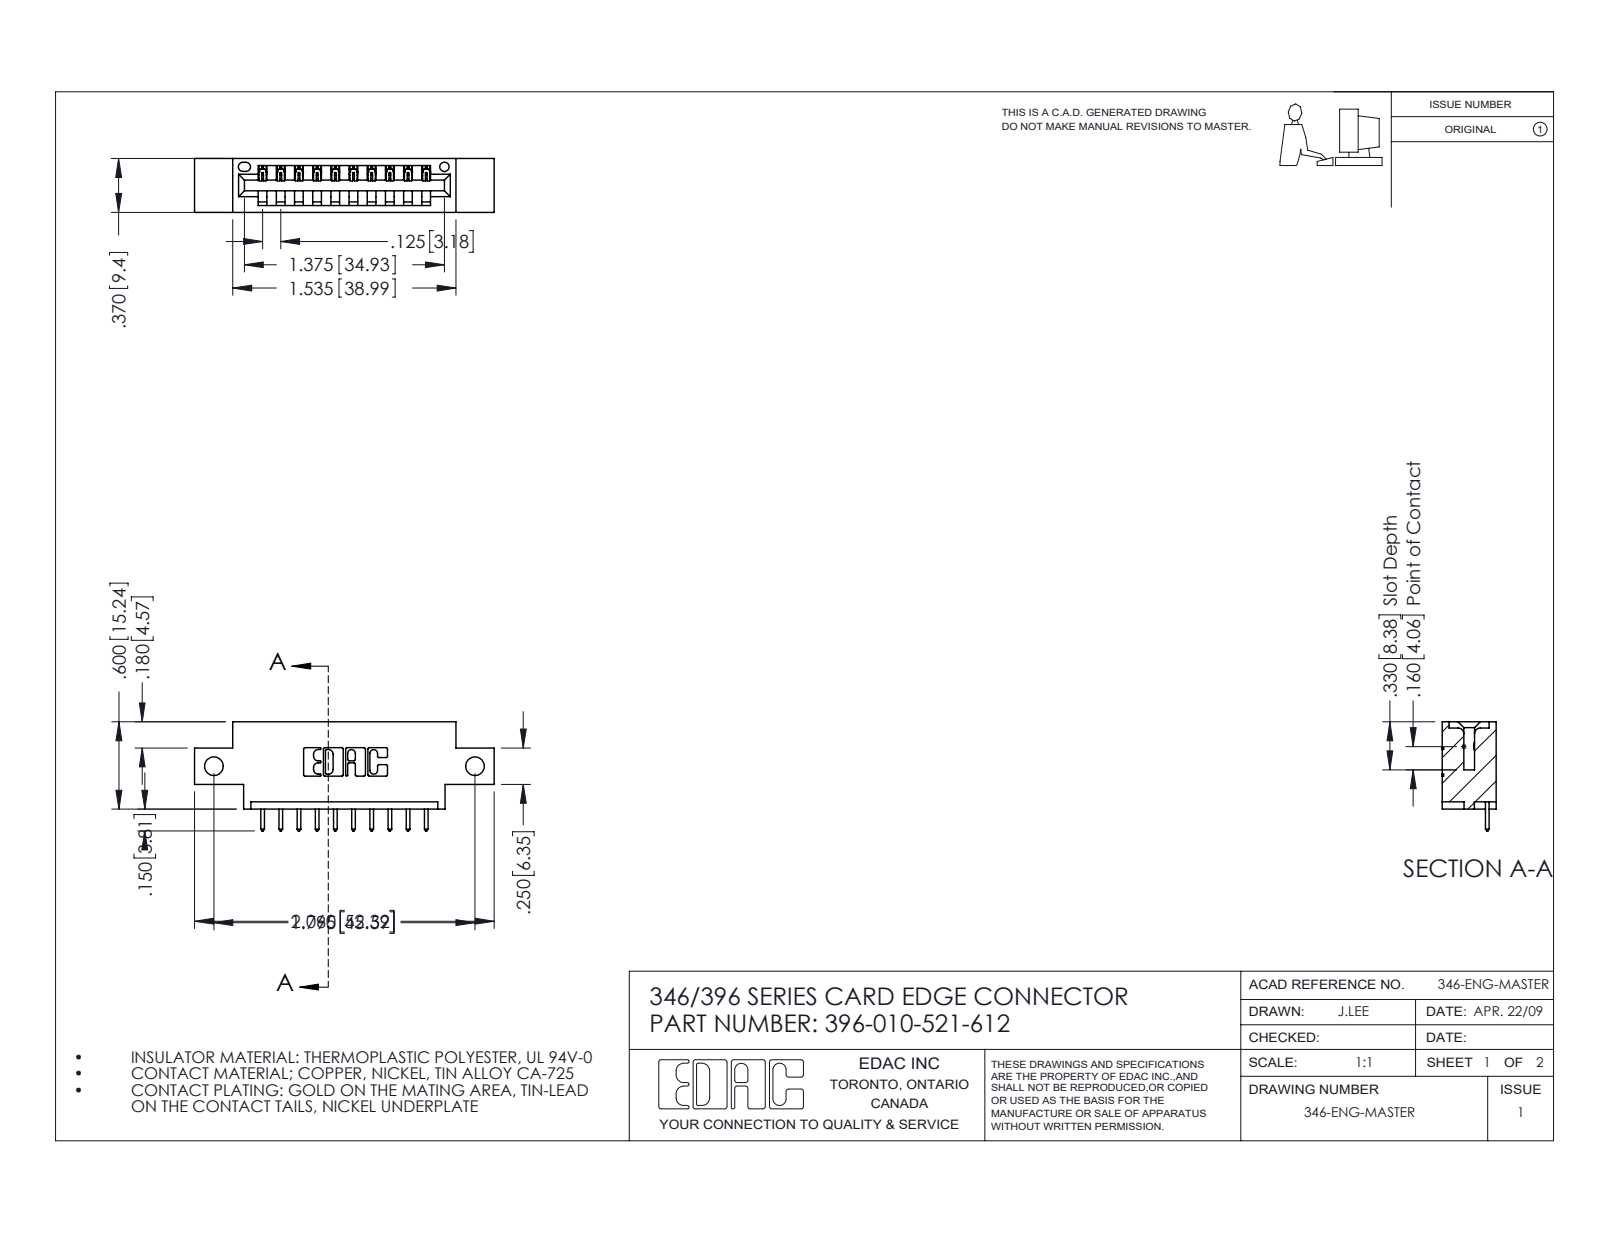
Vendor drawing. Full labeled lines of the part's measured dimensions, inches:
Part name (STEP PRODUCT): 396-010-521-612; 345-292-001_345-293-121; 346 Part_0.170 Offset - Side Mount
STEP written by: SolidWorks 2016 (CONFIG_CONTROL_DESIGN)
Units: inches
Bodies: 11 solids, 706 faces (480 planar, 226 cylindrical, 0 other)
Overall size (bounding box): 2.06 × 0.75 × 0.37
Volume: 0.276 in³ · Surface area: 8.064 in²
Round holes (diameter × count): ⌀0.128 ×2, ⌀0.064 ×1
Partial cylindrical surfaces — rounded edges, fillets, slot ends (radius × count): R0.01 ×22, R0.006 ×20, R0.01 ×20, R0.007 ×6, R0.031 ×6, R0.026 ×3, R0.031 ×2, R0.04 ×2
Main face-to-face distances: 0.25, 0.37, 0.048, 0.322, 0.148, 0.222, 0.1, 0.174, 0.072, 0.298
Hole centre spacings: 1.795
